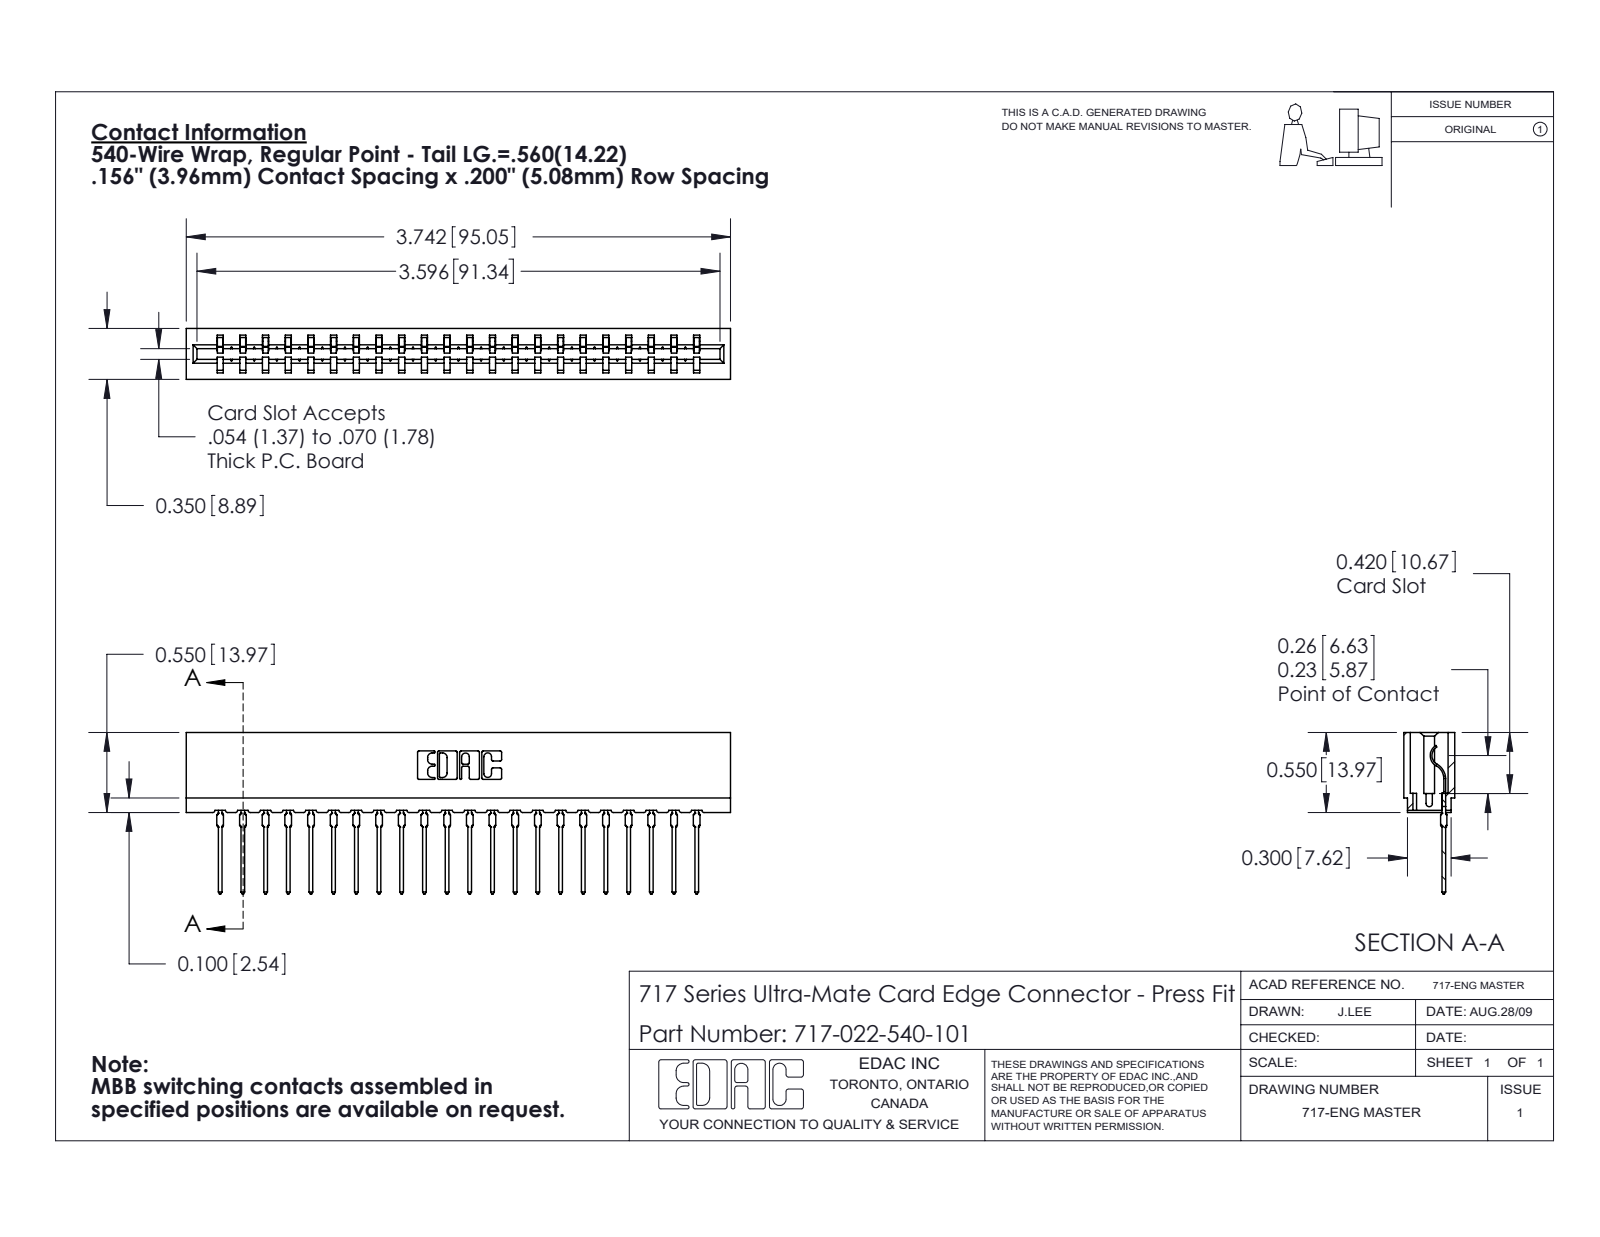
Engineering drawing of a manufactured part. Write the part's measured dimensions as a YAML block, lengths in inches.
part_name: "717 Part_Insulator Option - 06; 745-292-001_540; 717-022-540-101"
step_written_by: "SolidWorks 2020 (CONFIG_CONTROL_DESIGN)"
units: inches
bodies: {solids: 23, faces: 2580, planar: 1550, cylindrical: 458, other: 572}
overall_size: [3.742, 1.109, 0.35]
volume: 0.498
surface_area: 17.84
partial_cylinders:
  - {radius: 0.015, count: 44}
  - {radius: 0.021, count: 44}
  - {radius: 0.01, count: 22}
  - {radius: 0.007, count: 6}
  - {radius: 0.031, count: 6}
  - {radius: 0.005, count: 4}
  - {radius: 0.011, count: 4}
  - {radius: 0.026, count: 3}
face_to_face_distances: [0.212, 0.138, 0.35, 0.156, 0.074, 0.063, 0.287, 0.076, 0.149, 0.624]
